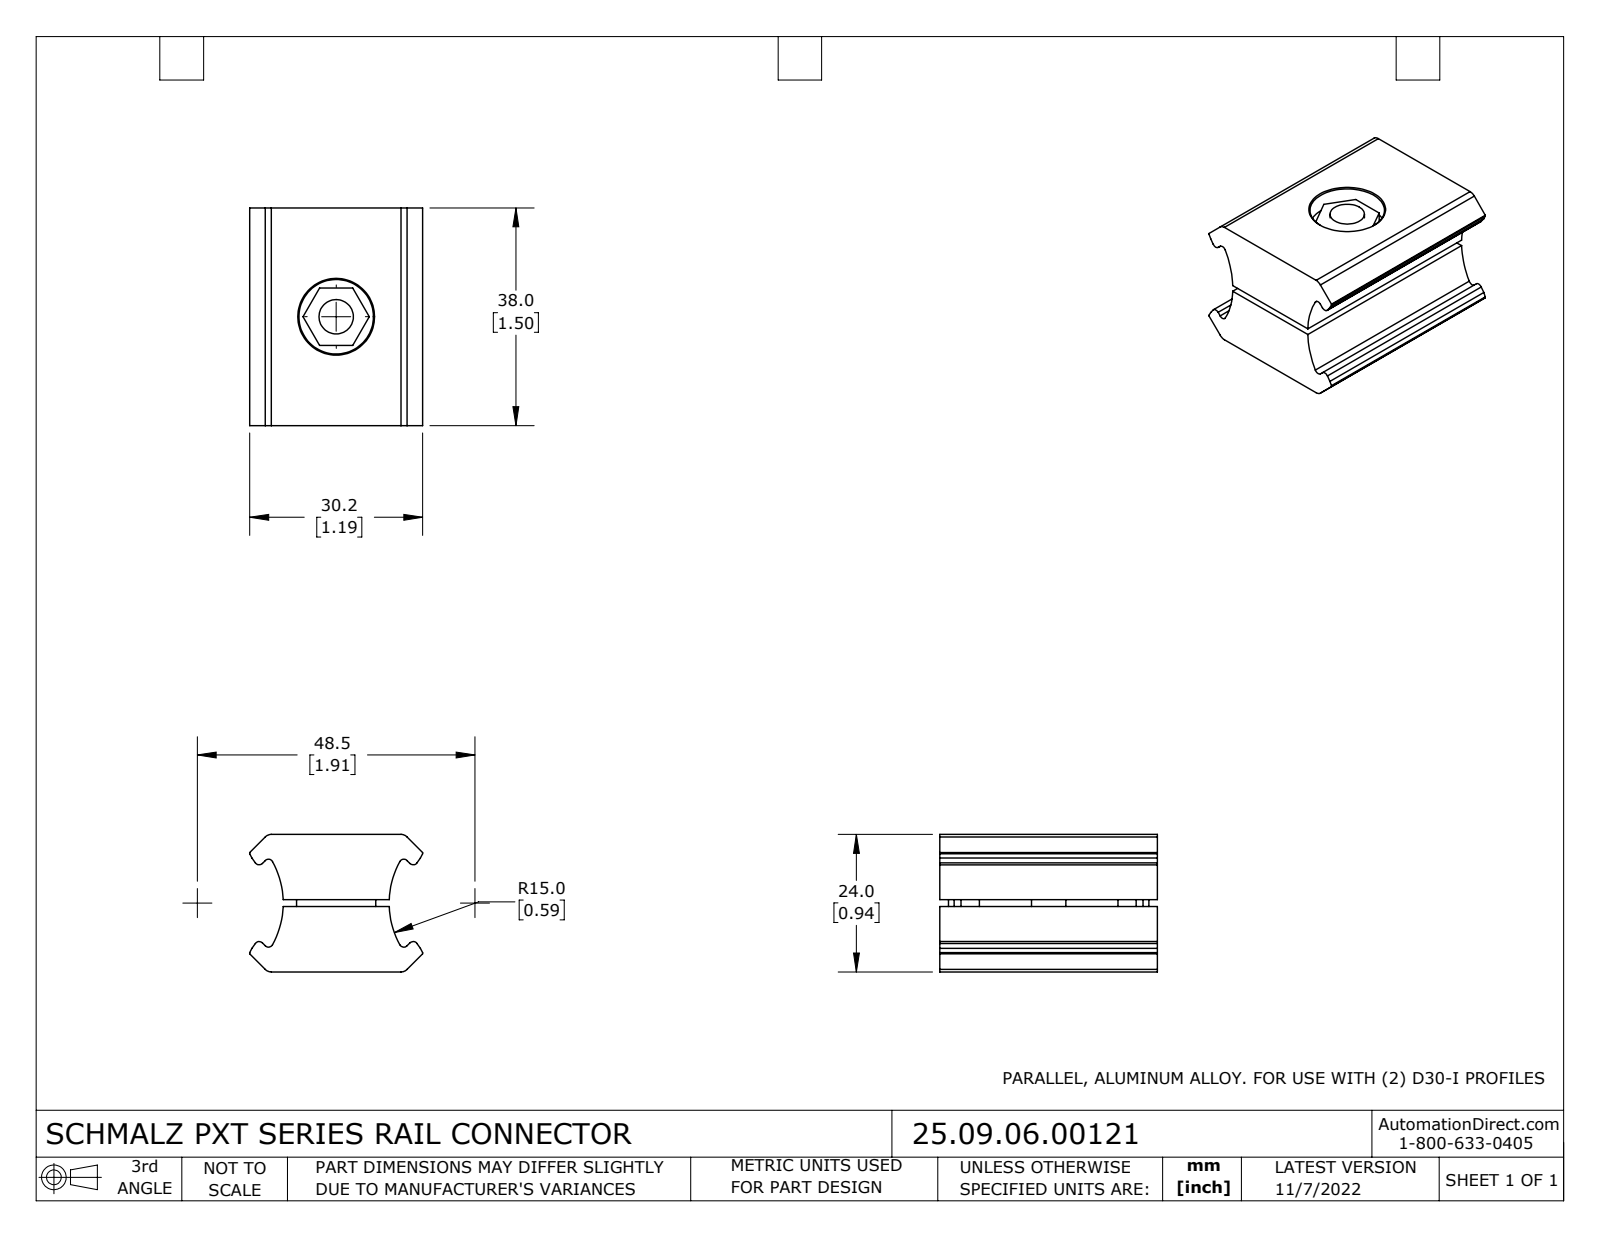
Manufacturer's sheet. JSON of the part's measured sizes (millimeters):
{"part_name": "25.09.06.00121", "step_written_by": "SolidWorks 2021 (CONFIG_CONTROL_DESIGN)", "units": "millimeters", "bodies": {"solids": 3, "faces": 96, "planar": 64, "cylindrical": 30, "other": 2}, "overall_size": [38, 30.2, 24], "volume_mm3": 19911, "surface_area_mm2": 8374, "round_holes": [[5, 1], [6, 1], [13, 1]], "round_bosses_or_shafts": [[10, 1]], "partial_cylinders_radius": [[0.8, 8], [1.5, 4], [15, 2]], "face_to_face_distances": [11.4, 12.6, 24, 1.2, 38, 33.86, 7, 4.4, 17, 5.6]}
